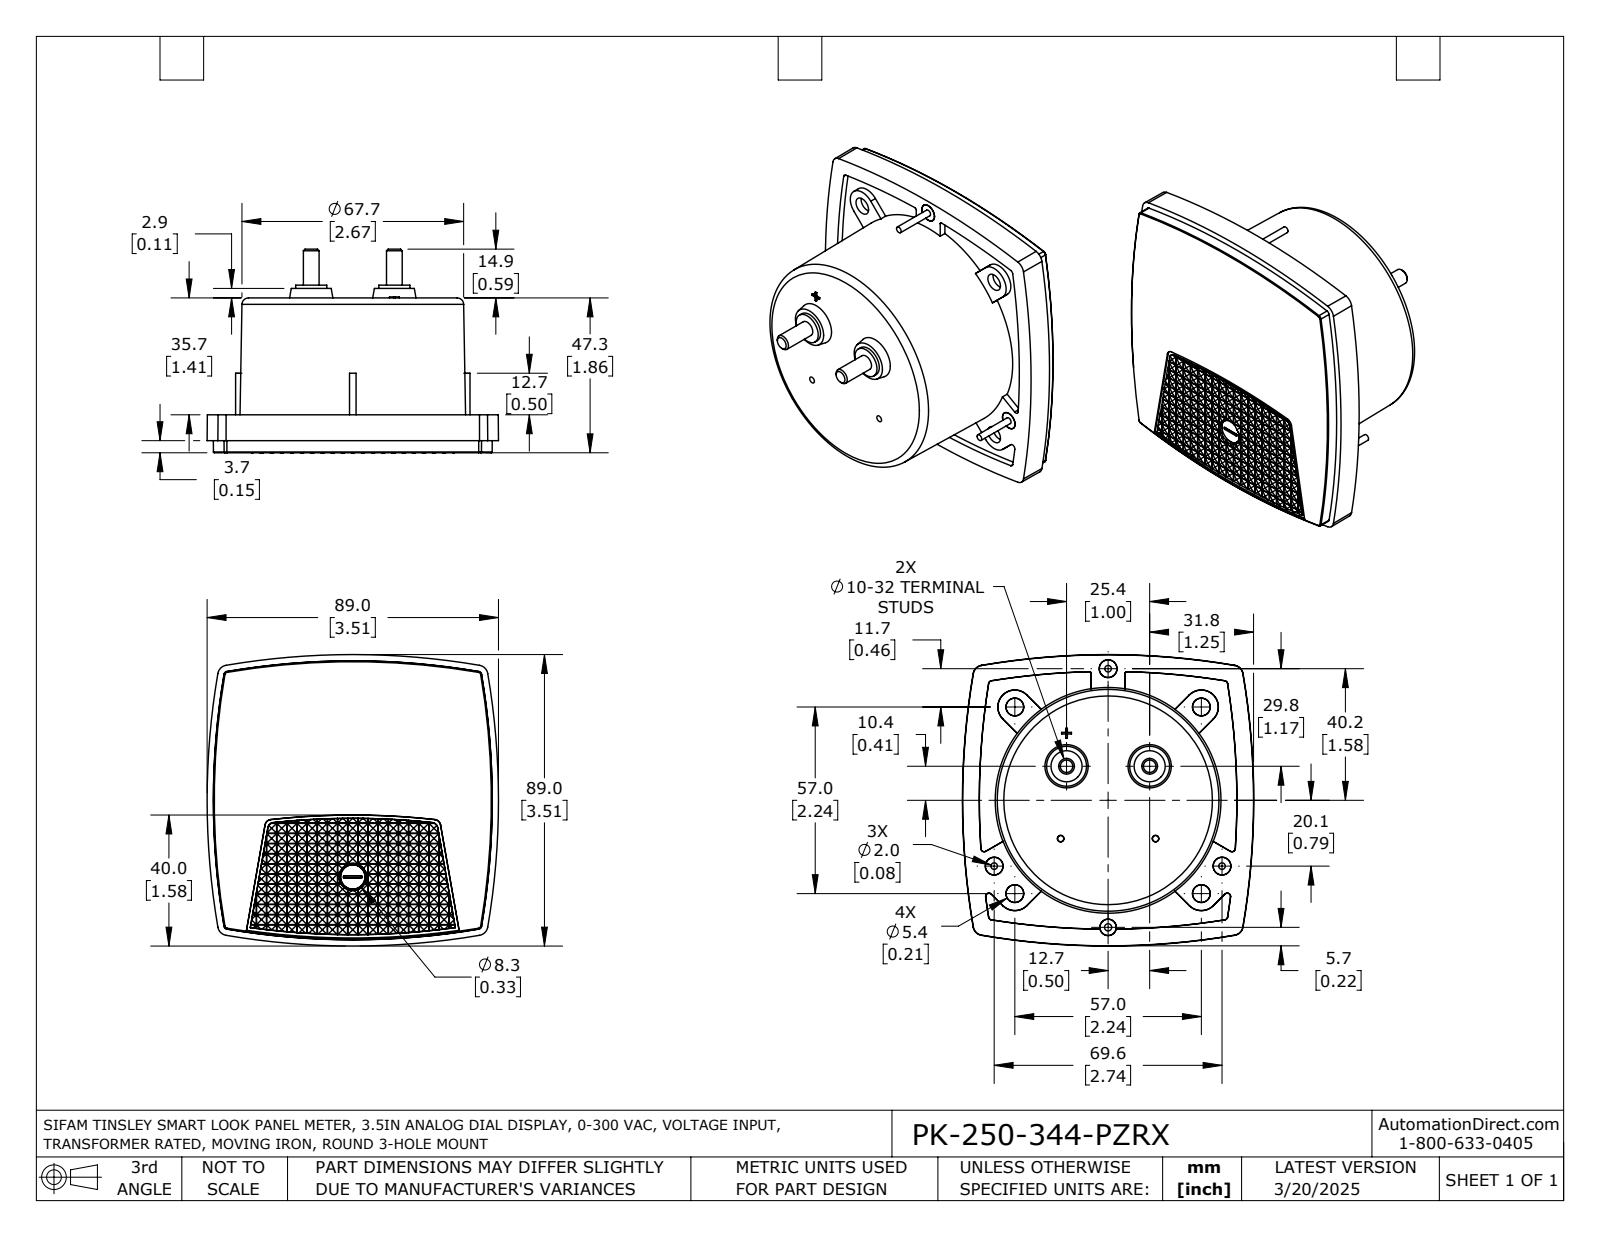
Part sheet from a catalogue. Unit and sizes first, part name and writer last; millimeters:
Units: millimetres
Overall size (bounding box): 89 × 89 × 62.3
Round holes (diameter × count): ⌀2.2 ×1
Round bosses / shafts (diameter × count): ⌀5.4 ×3, ⌀2 ×3, ⌀9.5 ×2, ⌀4.8 ×2
Partial cylindrical surfaces — rounded edges, fillets, slot ends (radius × count): R227.6 ×1
Main face-to-face distances: 47.3, 35.7, 11.6, 2, 37.7, 9.6, 0.6, 2.4, 1.8, 3
Volume: 212 900 mm³ · Surface area: 28 570 mm²
Bodies: 1 solid, 1078 faces (950 planar, 23 cylindrical, 105 other)
Part name (STEP PRODUCT): PK-250-344-PZRX
STEP written by: SolidWorks 2021 (AUTOMOTIVE_DESIGN)
